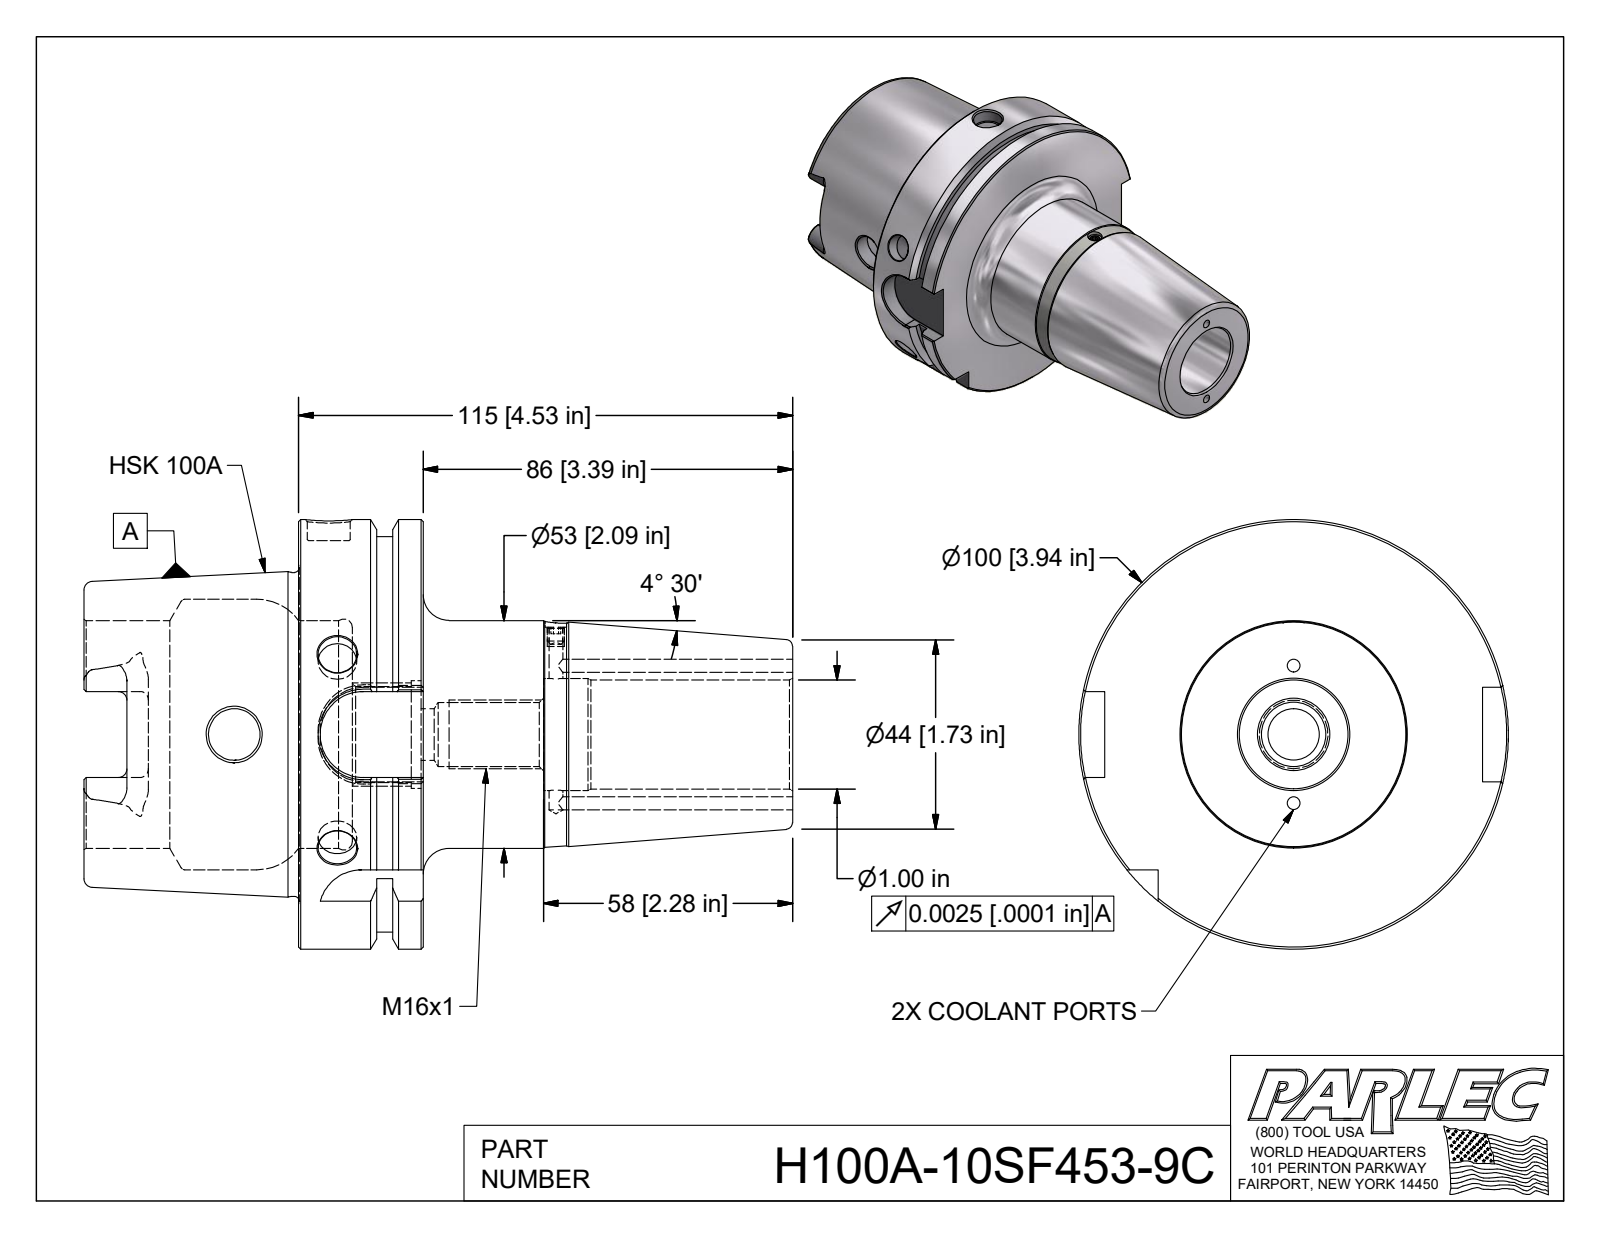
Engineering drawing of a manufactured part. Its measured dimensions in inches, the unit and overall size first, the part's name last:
Units: inches
Overall size (bounding box): 6.496 × 3.937 × 3.937
Round holes (diameter × count): ⌀0.118 ×2, ⌀0.354 ×2, ⌀0.472 ×2, ⌀0.128 ×1, ⌀0.197 ×1, ⌀0.394 ×1, ⌀0.587 ×1, ⌀0.881 ×1, ⌀0.985 ×1, ⌀0.999 ×1, ⌀1.029 ×1, ⌀2.087 ×1
Round bosses / shafts (diameter × count): ⌀3.937 ×1, ⌀3.622 ×1, ⌀2.967 ×1
Partial cylindrical surfaces — rounded edges, fillets, slot ends (radius × count): R0.079 ×6, R0.192 ×4, R0.394 ×4
Main face-to-face distances: 1.142, 0.492, 0.65, 1.969, 2.461, 3.11, 6.496, 4.528, 4.035, 3.386
Hole centre spacings: 0.63, 1.26, 2.082
Volume: 23.75 in³ · Surface area: 107.4 in²
Bodies: 1 solid, 152 faces (49 planar, 42 cylindrical, 61 other)
STEP written by: Autodesk Inventor 2018 (AUTOMOTIVE_DESIGN)
